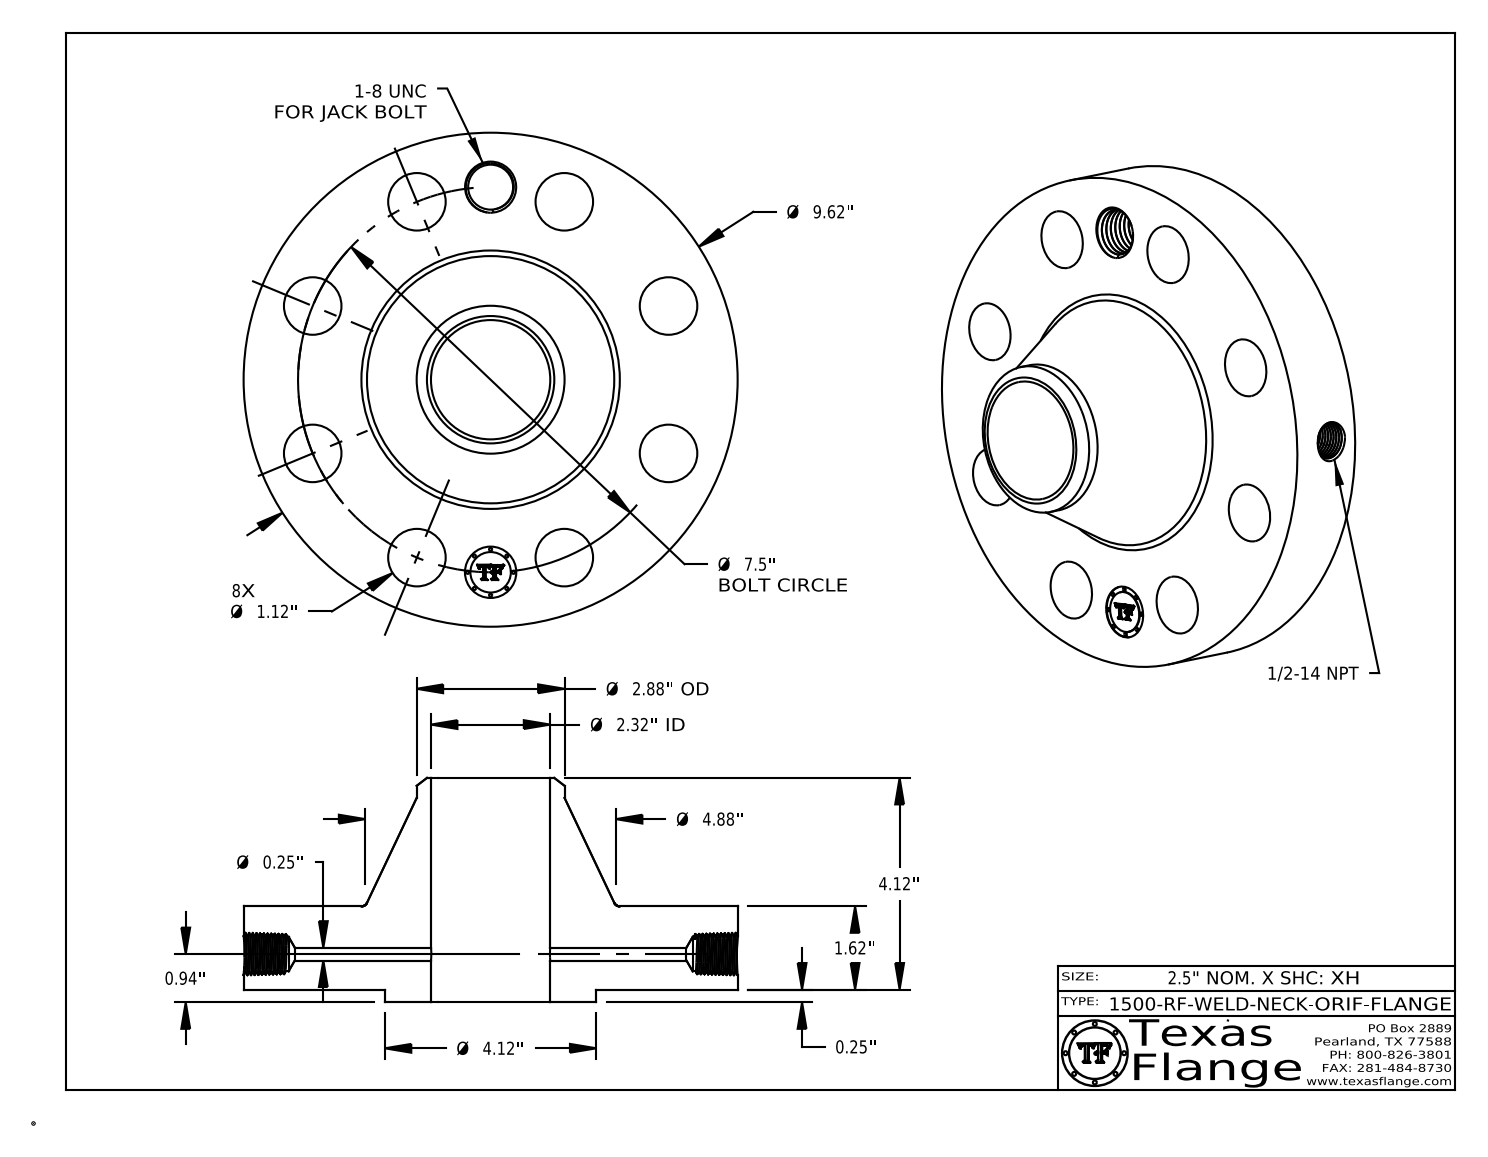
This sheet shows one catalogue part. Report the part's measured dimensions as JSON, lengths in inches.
{"part_name": "1500-RF-WELD-NECK", "step_written_by": "CATIA V5 STEP AP214 (AUTOMOTIVE_DESIGN)", "units": "inches", "bodies": {"solids": 1, "faces": 759, "planar": 369, "cylindrical": 89, "other": 301}, "overall_size": [9.62, 9.62, 4.37], "volume_in3": 115.6, "surface_area_in2": 285.9, "round_holes": [[1.12, 8], [0.25, 1], [0.672, 1], [0.875, 1], [1, 1], [2.323, 1]], "round_bosses_or_shafts": [[0.061, 8], [9.62, 1], [4.12, 1], [2.88, 1], [0.788, 1]], "face_to_face_distances": [1.62, 0.25, 1.87, 4.37, 4.12, 2.5, 1.855, 1.605, 0.015, 2.515], "hole_center_spacings": [3.75, 2.87, 5.303, 6.929, 7.5, 1.463, 4.167, 6.236]}
